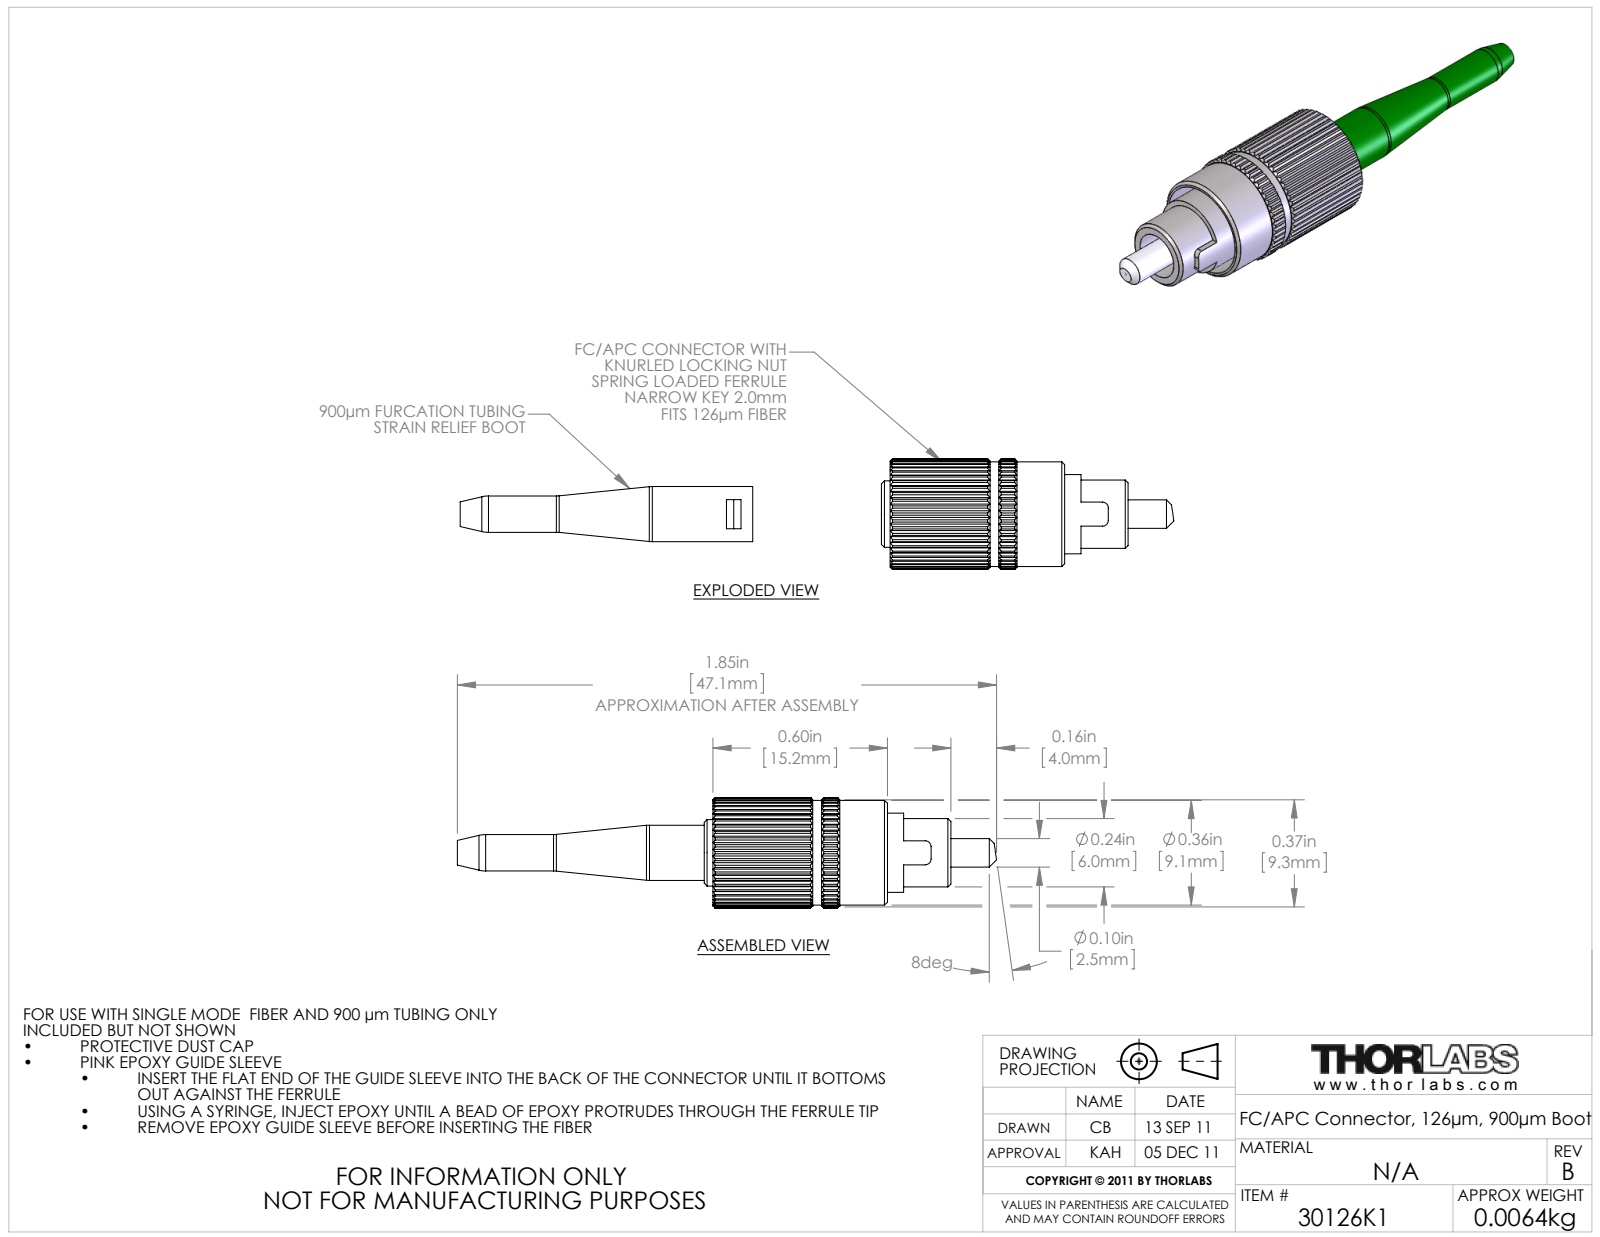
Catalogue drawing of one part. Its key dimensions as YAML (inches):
part_name: "14009-E0W"
step_written_by: "SolidWorks 2011 (AUTOMOTIVE_DESIGN)"
units: inches
bodies: {solids: 3, faces: 422, planar: 240, cylindrical: 146, other: 36}
overall_size: [1.853, 0.38, 0.38]
volume: 0.072
surface_area: 3.441
round_holes:
  - {diameter: 0.04, count: 1}
  - {diameter: 0.057, count: 1}
  - {diameter: 0.098, count: 1}
  - {diameter: 0.126, count: 1}
  - {diameter: 0.137, count: 1}
  - {diameter: 0.164, count: 1}
  - {diameter: 0.193, count: 1}
  - {diameter: 0.2, count: 1}
  - {diameter: 0.325, count: 1}
round_bosses_or_shafts:
  - {diameter: 0.36, count: 1}
  - {diameter: 0.313, count: 1}
  - {diameter: 0.273, count: 1}
  - {diameter: 0.235, count: 1}
  - {diameter: 0.229, count: 1}
  - {diameter: 0.19, count: 1}
  - {diameter: 0.125, count: 1}
partial_cylinders:
  - {radius: 0.02, count: 2}
  - {radius: 0.12, count: 1}
  - {radius: 0.19, count: 1}
face_to_face_distances: [0.28, 0.281, 0.025, 0.25, 0.275, 0.127, 0.123, 0.148, 0.28, 0.133]
